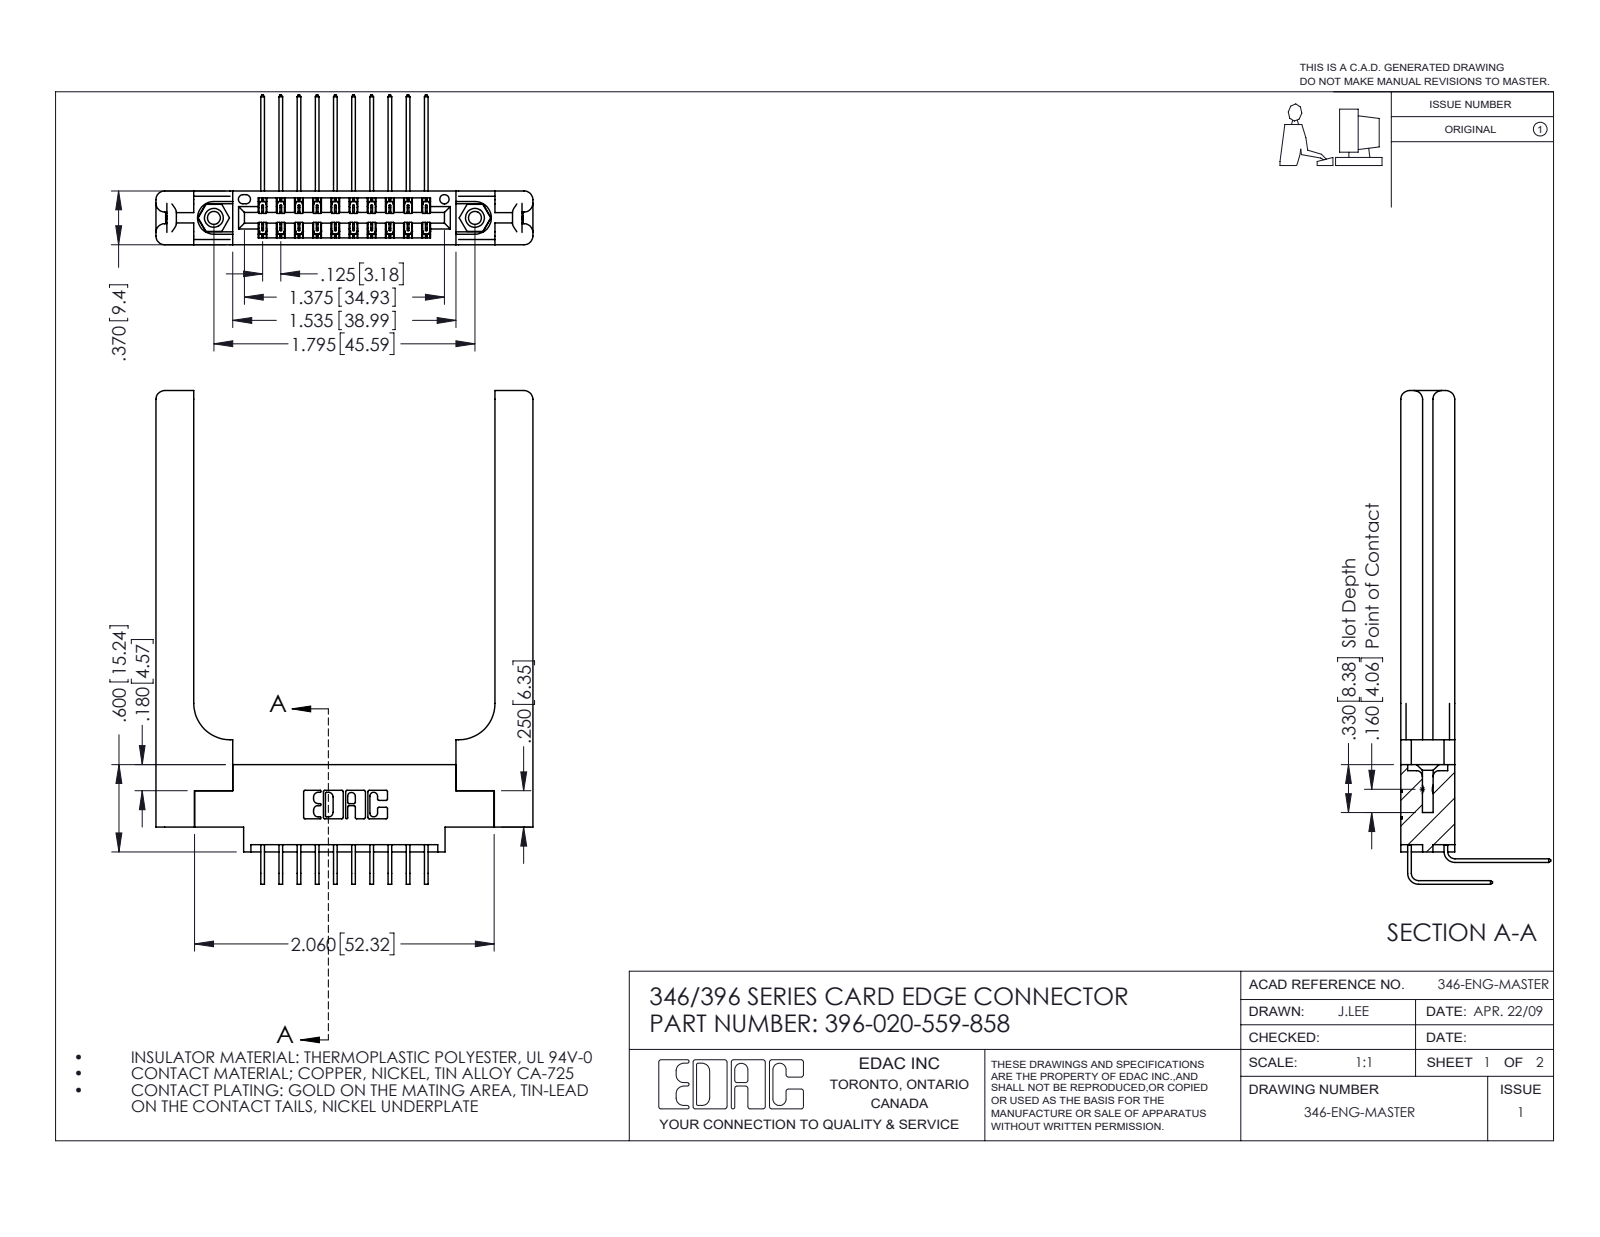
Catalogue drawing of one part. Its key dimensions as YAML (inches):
part_name: "396-020-559-858; 346-220-058_345-220-058; 345-250-001_345-250-001-102; 345-292-001_559 Tail - 2 (+2 more)"
step_written_by: "SolidWorks 2016 (CONFIG_CONTROL_DESIGN)"
units: inches
bodies: {solids: 25, faces: 1462, planar: 968, cylindrical: 434, other: 60}
overall_size: [3.393, 2.591, 1.03]
volume: 0.831
surface_area: 21.12
round_holes:
  - {diameter: 0.089, count: 2}
  - {diameter: 0.125, count: 2}
  - {diameter: 0.156, count: 2}
  - {diameter: 0.064, count: 1}
round_bosses_or_shafts:
  - {diameter: 0.155, count: 2}
partial_cylinders:
  - {radius: 0.006, count: 30}
  - {radius: 0.01, count: 22}
  - {radius: 0.06, count: 16}
  - {radius: 0.007, count: 6}
  - {radius: 0.031, count: 6}
  - {radius: 0.026, count: 3}
  - {radius: 0.014, count: 2}
  - {radius: 0.022, count: 2}
face_to_face_distances: [0.37, 0.15, 0.072, 0.148, 0.048, 0.22, 0.322, 0.102, 0.173, 0.25]
hole_center_spacings: [0.246, 1.59, 1.795]
